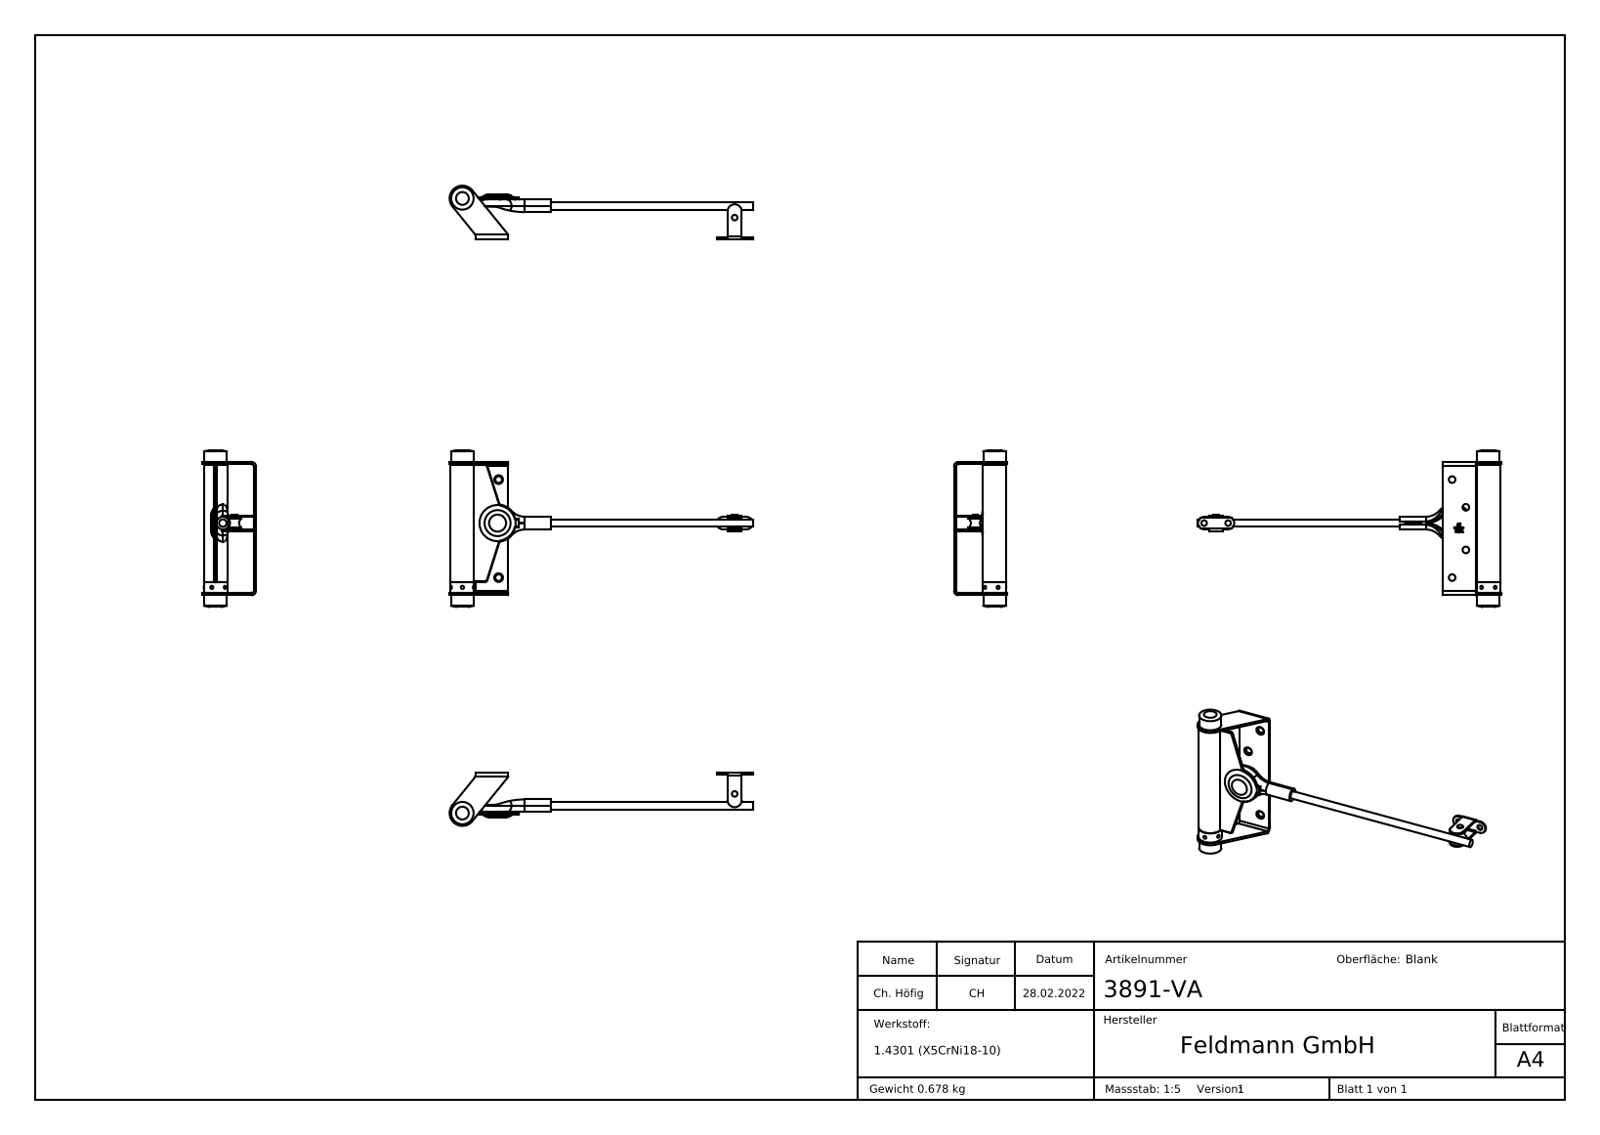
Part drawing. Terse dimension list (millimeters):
name: 389x Teil4_389x-VA Teil4; 389x Teil5_3891-VA Teil5; 389x Teil3_389x-VA Teil3; 389x Teil2_389x-VA Teil2 (+4 more)
written by: SolidWorks 2018 (CONFIG_CONTROL_DESIGN)
unit: mm
bodies: 9 solids, 560 faces (245 planar, 105 cylindrical, 210 other)
size: 285 × 147 × 50
volume: 86 916 mm³; area: 44 968 mm²
holes: 6× ⌀3, 4× ⌀6.2, 2× ⌀5.2, 1× ⌀7, 1× ⌀10
bosses: 1× ⌀22, 1× ⌀21, 1× ⌀13, 1× ⌀12, 1× ⌀5.2, 1× ⌀2.8
rounds: 25× R0.2, 17× R0.5, 8× R2, 2× R1, 2× R2.5, 2× R4, 2× R5.85, 2× R21.02
face distances: 2, 37, 123, 35, 39, 125, 121, 1.5, 49.15, 60.85
hole spacings: 29.02, 67.25, 22.5, 35.21, 40, 41.02, 78.08, 92
